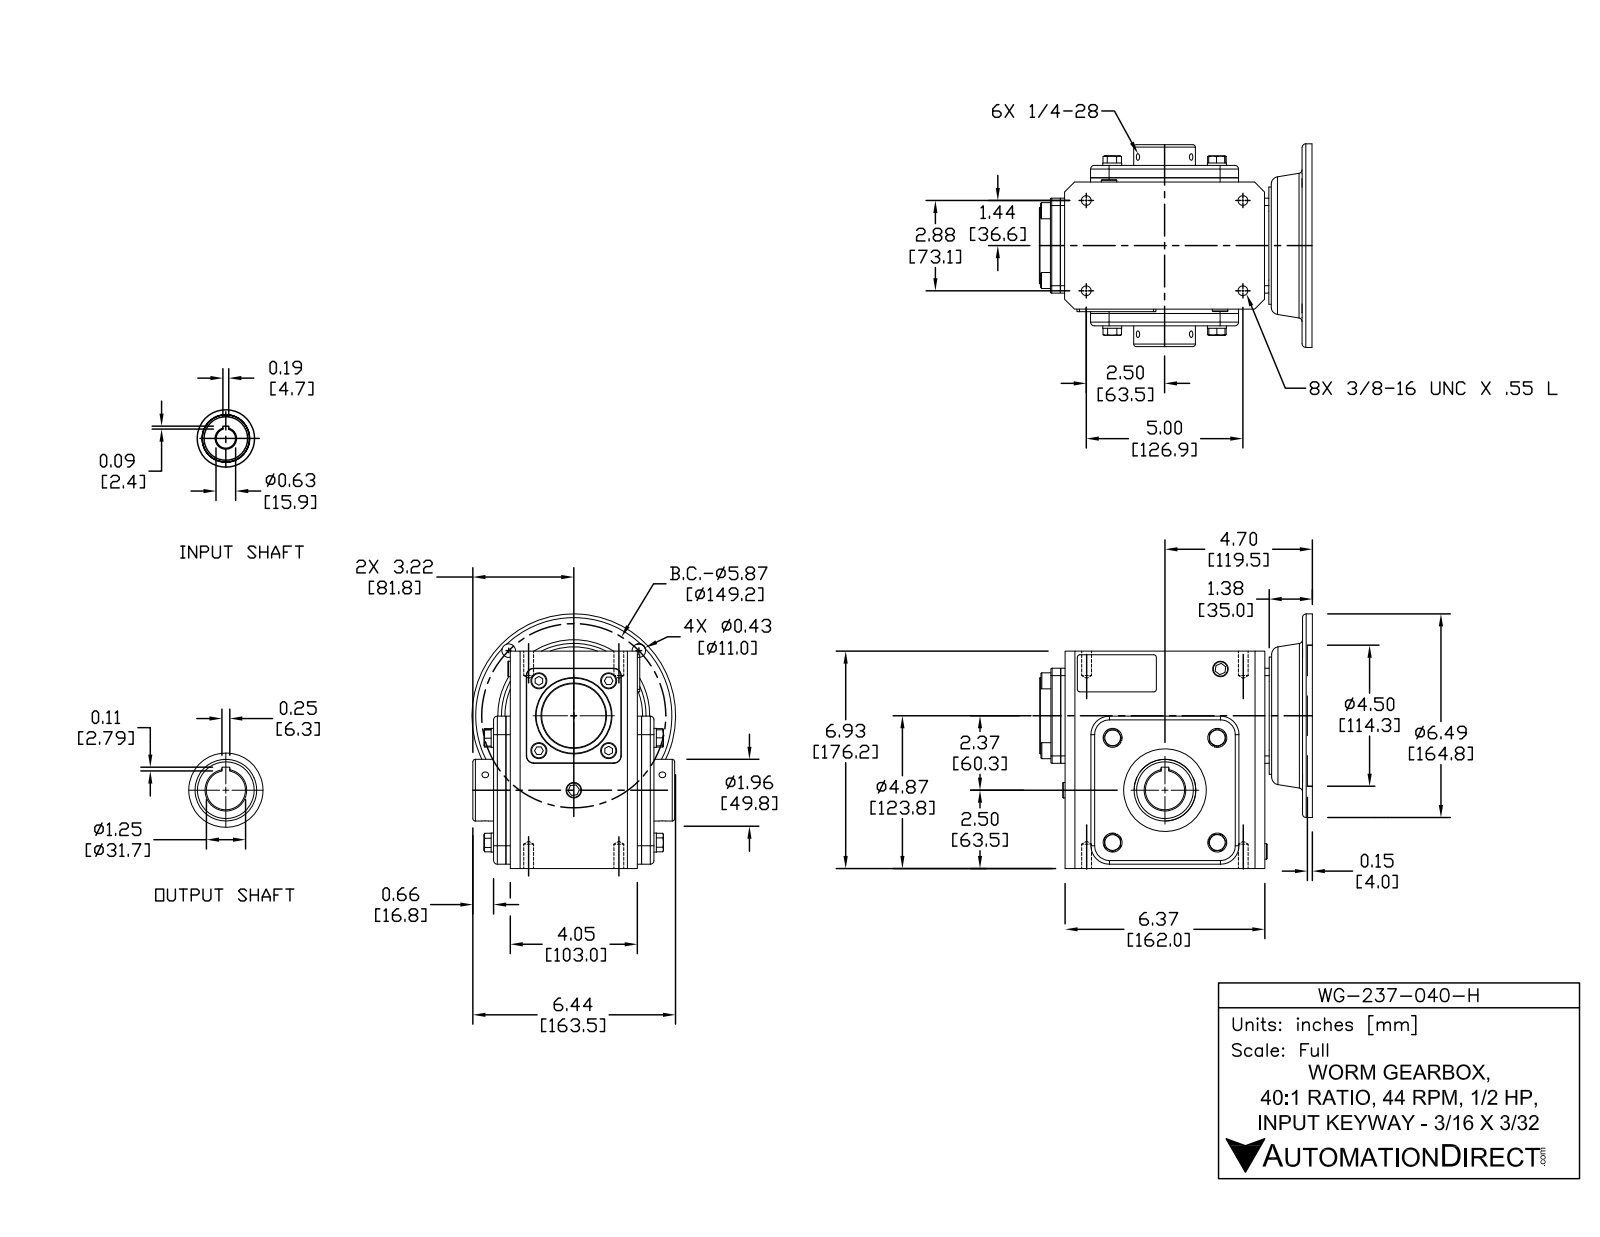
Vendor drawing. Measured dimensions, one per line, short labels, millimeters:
name: WG-237-040-H
written by: SolidWorks 2015 (CONFIG_CONTROL_DESIGN)
unit: mm
bodies: 37 solids, 609 faces (348 planar, 172 cylindrical, 89 other)
size: 221 × 206.3 × 165
volume: 3 558 000 mm³; area: 348 800 mm²
holes: 6× ⌀5.4, 4× ⌀8, 4× ⌀10.3, 1× ⌀15, 1× ⌀15.9, 1× ⌀30, 1× ⌀31.8, 1× ⌀37, 1× ⌀50, 1× ⌀67, 1× ⌀97, 1× ⌀114.3
bosses: 4× ⌀15.4, 4× ⌀13, 1× ⌀165, 1× ⌀95, 1× ⌀62, 1× ⌀52, 1× ⌀29
rounds: 8× R2, 8× R3, 6× R6, 4× R15, 2× R0.5, 2× R1
face distances: 3.5, 110, 120, 13.5, 10, 106.5, 116.5, 165.5, 8, 176.2
hole spacings: 72.6, 74.6, 125.6, 143.6, 53.3, 73.2, 105.5, 105.5
